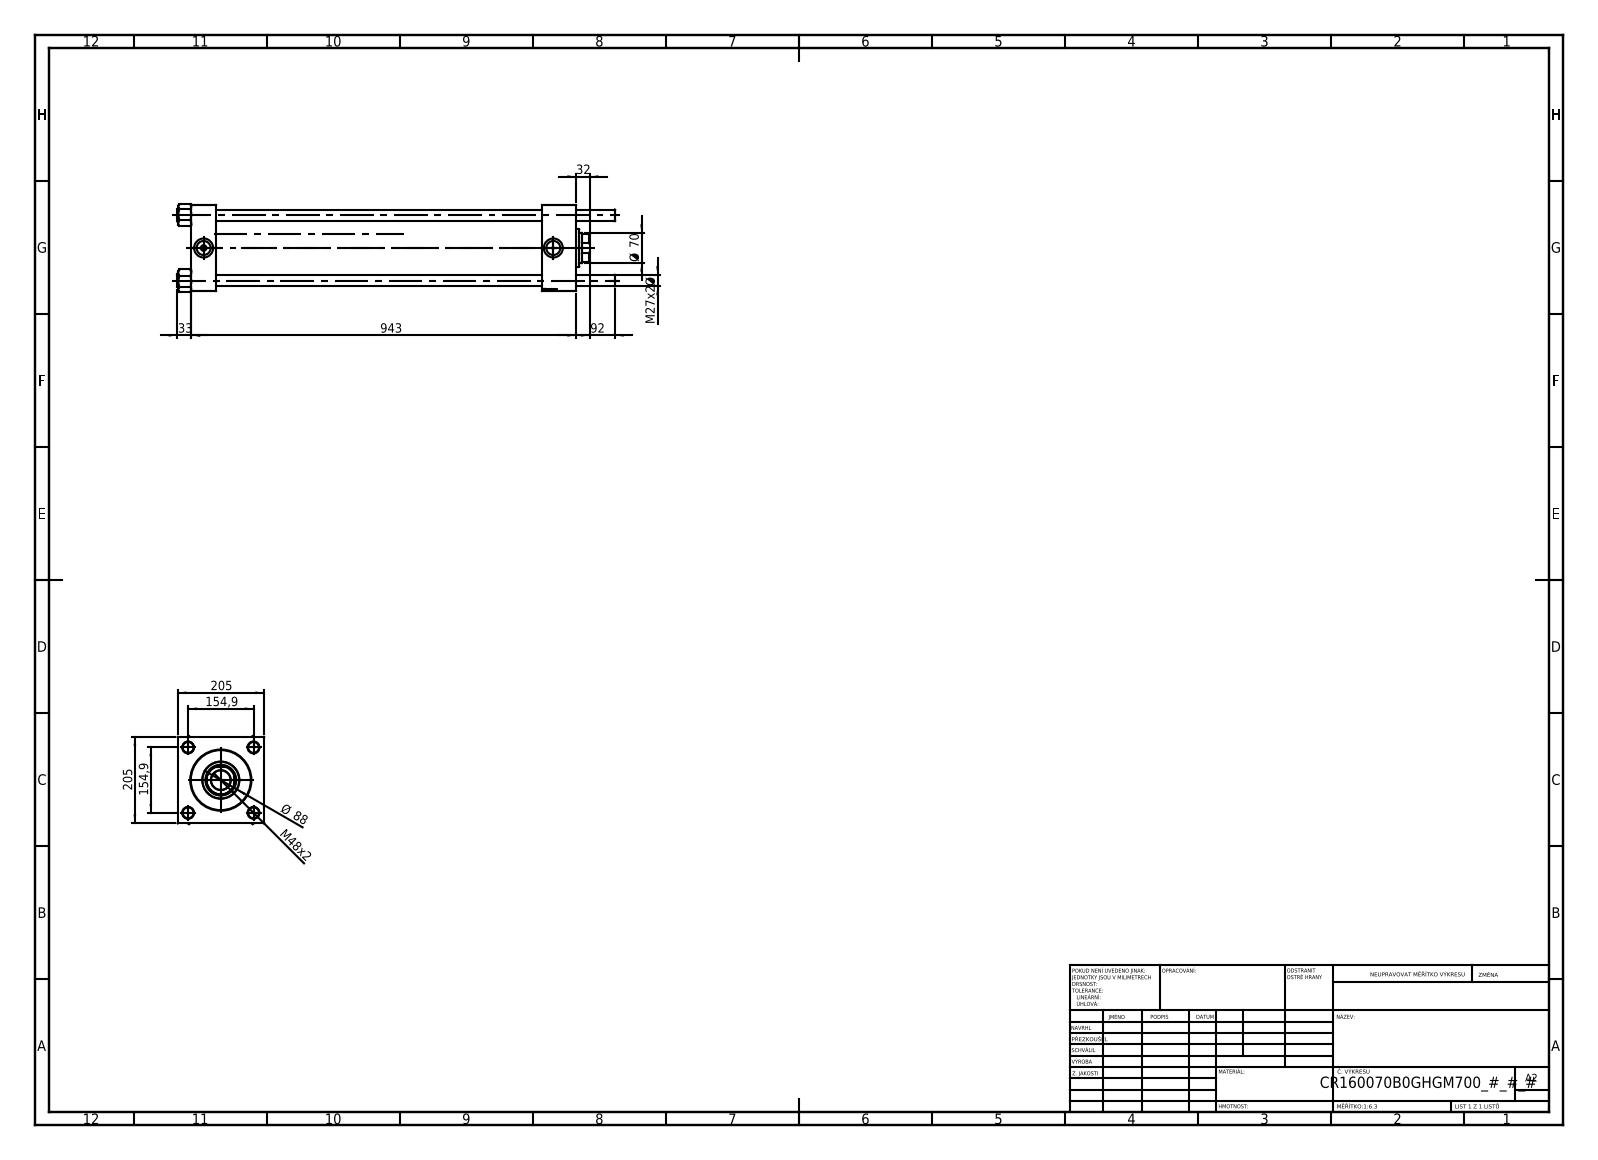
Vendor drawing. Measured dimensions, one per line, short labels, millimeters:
name: V215CR_VCP_B; NUT_M5_B; V215CR_B-1; V215CR_B_TYCINKA (+1 more)
written by: SolidWorks 2019 (CONFIG_CONTROL_DESIGN)
unit: mm
bodies: 11 solids, 1206 faces (480 planar, 78 cylindrical, 648 other)
size: 1036 × 207.94 × 205
volume: 12 970 000 mm³; area: 1 831 000 mm²
holes: 4× ⌀27, 2× ⌀7, 2× ⌀33.24, 2× ⌀45, 1× ⌀46.5, 1× ⌀70, 1× ⌀73, 1× ⌀120, 1× ⌀142, 1× ⌀160
bosses: 4× ⌀30, 1× ⌀166, 1× ⌀88
rounds: 1× R34
face distances: 205, 58, 911, 853, 830, 772, 81, 882.3, 824.3, 52.3
hole spacings: 109.53, 154.9, 219.06, 828
